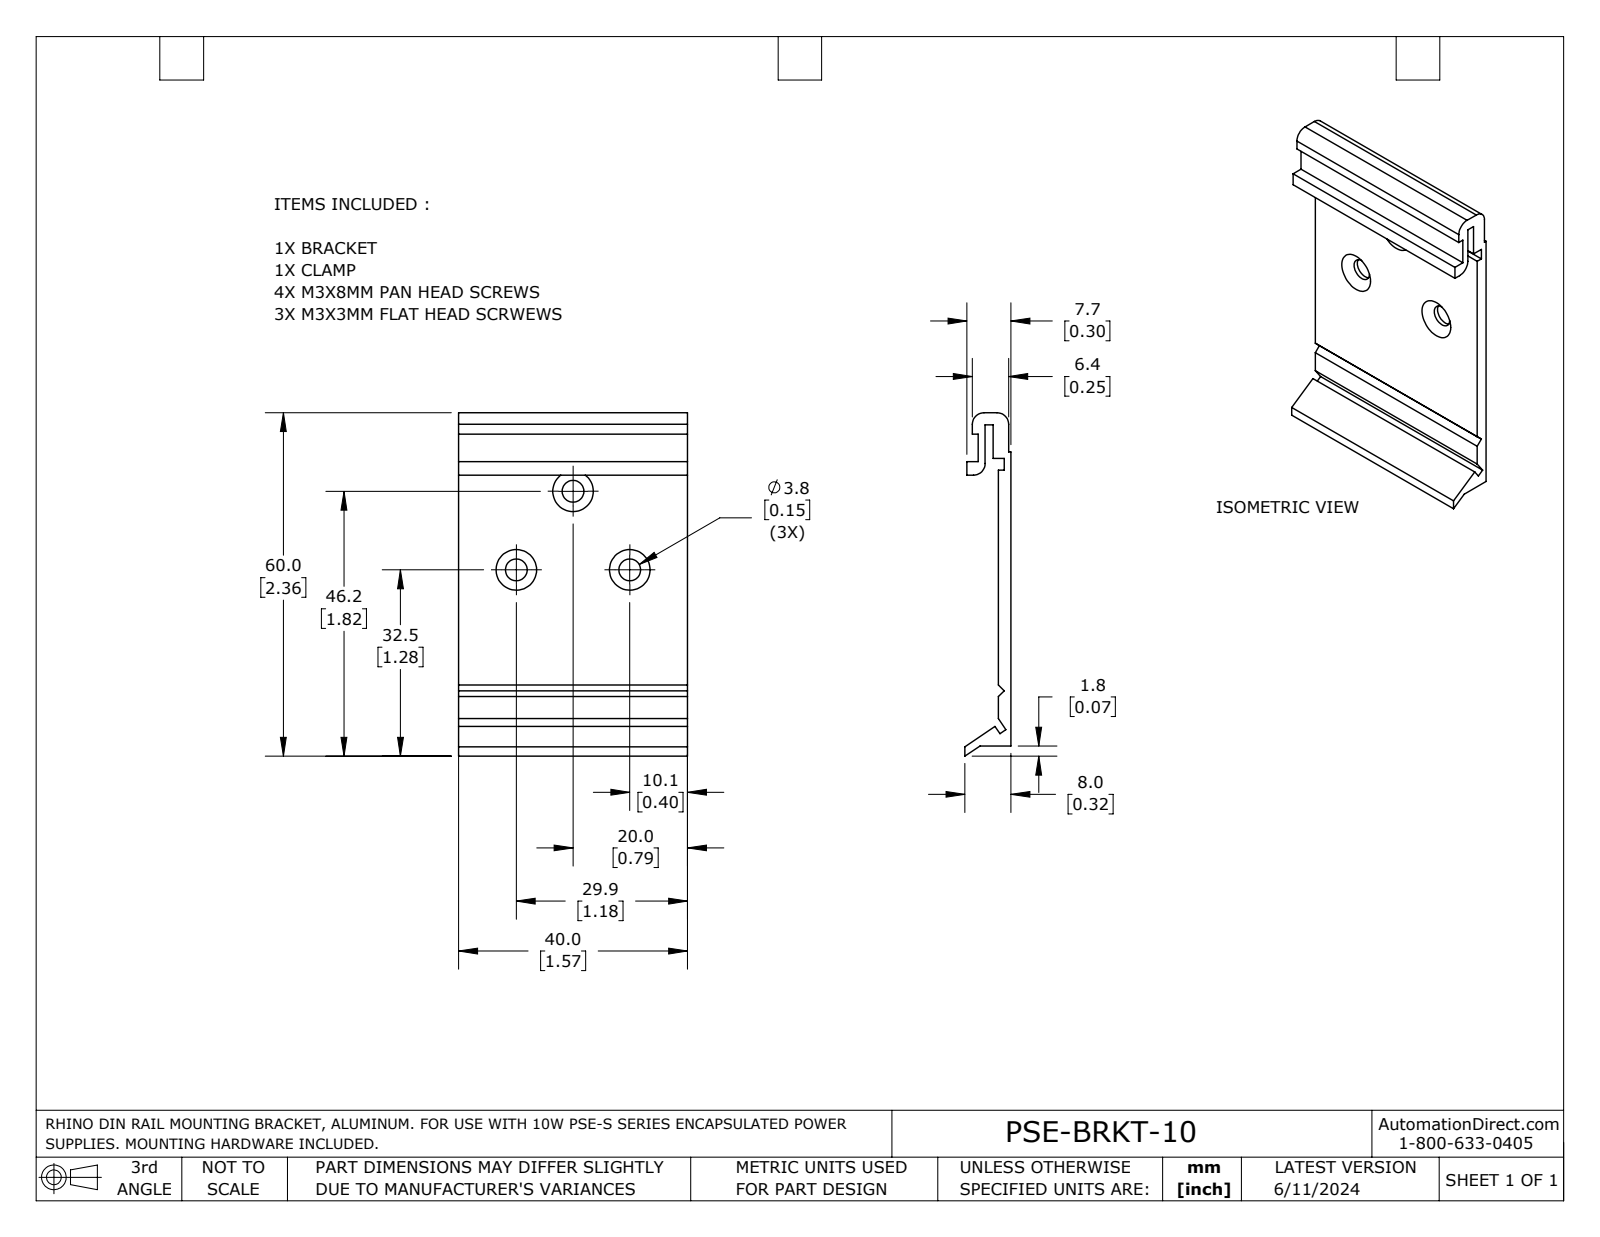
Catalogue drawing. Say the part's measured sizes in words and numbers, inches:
The part is named "PSE-BRKT-10". Its 3-D file was written by "SolidWorks 2023 (AUTOMOTIVE_DESIGN)". It is 1 solid with 38 faces: 29 planar, 6 cylindrical and 3 other. Overall it measures 2.361 by 1.574 by 0.317 inches. Its volume is 0.387 cubic inches and its surface area 10.78 square inches. Round holes: 3 of diameter 0.15. Partial cylindrical surfaces (rounded edges, fillets, slot ends): 3 of radius 0.08. The main face-to-face distances are 0.086, 0.091, 0.177, 0.139, 0.055, 0.037, 0.122, 0.162, 0.107, 0.07. The hole center spacings are 0.666, 0.78.
